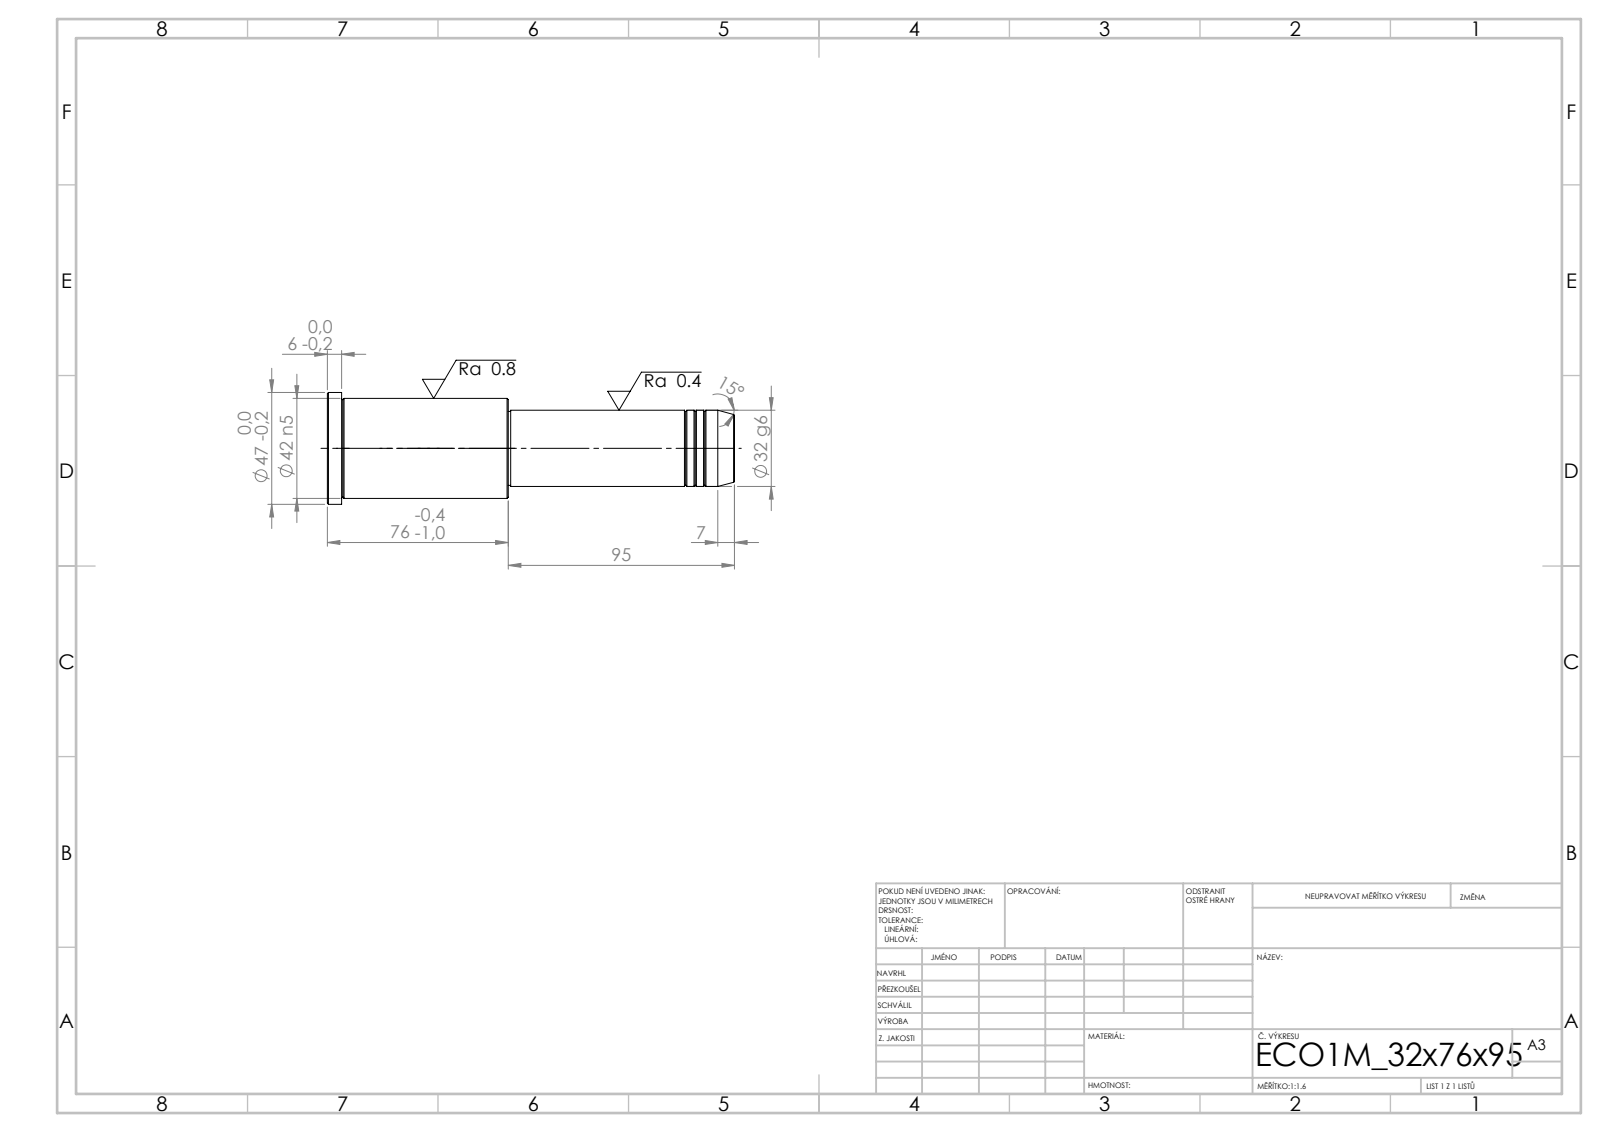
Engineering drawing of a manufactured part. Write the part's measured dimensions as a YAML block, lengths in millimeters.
step_written_by: "SolidWorks 2019 (CONFIG_CONTROL_DESIGN)"
units: millimeters
bodies: {solids: 1, faces: 43, planar: 5, cylindrical: 14, other: 24}
overall_size: [171, 47, 47]
volume: 182905
surface_area: 23185
round_bosses_or_shafts:
  - {diameter: 47, count: 1}
  - {diameter: 42, count: 1}
  - {diameter: 32, count: 1}
  - {diameter: 31, count: 1}
face_to_face_distances: [171, 95, 76, 165, 70, 6, 94, 1, 71, 77]
